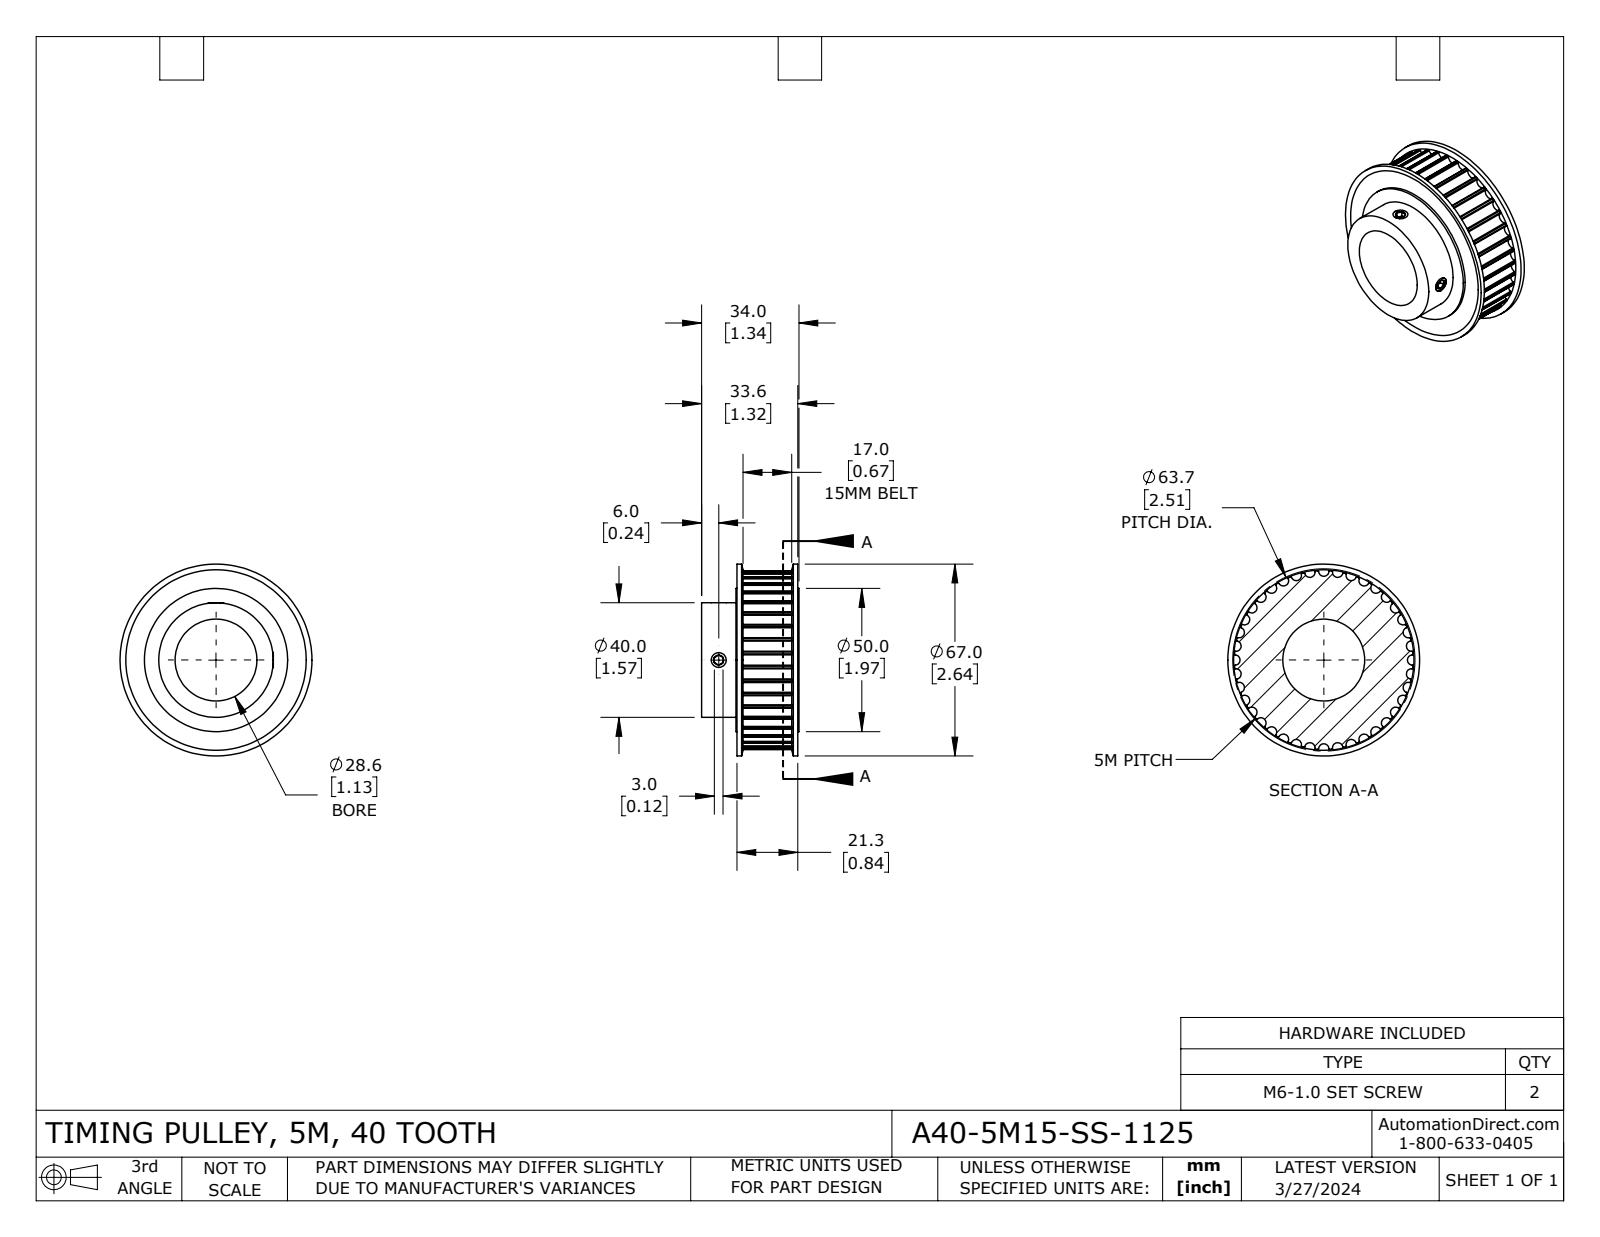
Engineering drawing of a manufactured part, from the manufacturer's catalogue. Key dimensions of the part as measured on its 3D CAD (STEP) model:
Part name (STEP PRODUCT): A40-5M15-SS-1125
STEP written by: SolidWorks 2021 (CONFIG_CONTROL_DESIGN)
Units: millimetres
Bodies: 5 solids, 282 faces (25 planar, 223 cylindrical, 34 other)
Overall size (bounding box): 67 × 67 × 34
Volume: 56 266 mm³ · Surface area: 22 381 mm²
Round holes (diameter × count): ⌀5 ×2, ⌀28.58 ×1, ⌀50 ×1
Round bosses / shafts (diameter × count): ⌀6 ×2, ⌀67 ×1, ⌀40 ×1
Partial cylindrical surfaces — rounded edges, fillets, slot ends (radius × count): R0.3 ×80, R1.82 ×40, R31.26 ×1
Main face-to-face distances: 1.6, 18.6, 2.5, 19.5, 17, 0.9, 21.1, 20.2, 22, 34
